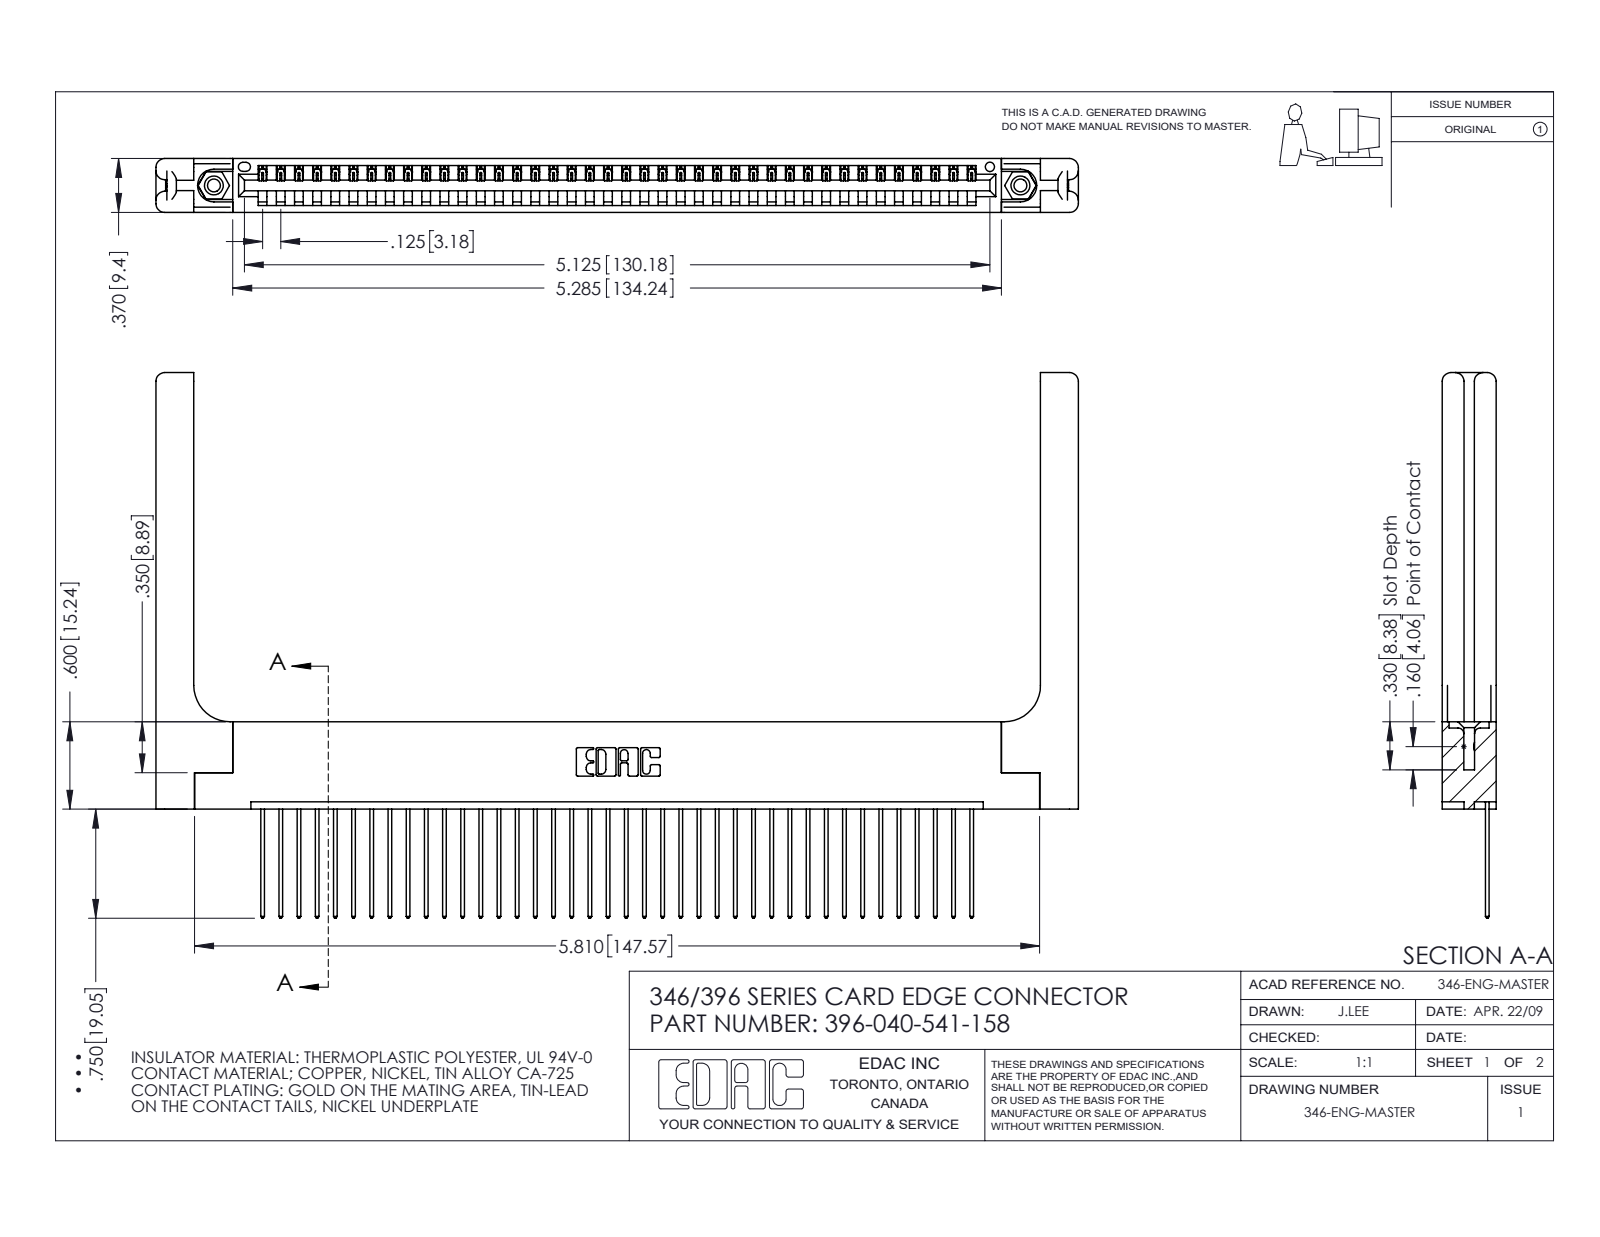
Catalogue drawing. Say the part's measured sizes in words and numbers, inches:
The part is named "345-250-001_345-250-001-102; 346-220-058_345-220-058; 346 Part_Flush Mounting Lugs - 0.156 Dia-TH; 345-292-001_345-293-141 (+1 more)". Its 3-D file was written by "SolidWorks 2016 (CONFIG_CONTROL_DESIGN)". It is 45 solids with 2698 faces: 1824 planar, 814 cylindrical and 60 other. Overall it measures 6.341 by 3.75 by 0.37 inches. Its volume is 1.407 cubic inches and its surface area 39.3 square inches. Round holes: 2 of diameter 0.089, 2 of diameter 0.125, 2 of diameter 0.156, 1 of diameter 0.064. Round bosses or shafts: 2 of diameter 0.155. Partial cylindrical surfaces (rounded edges, fillets, slot ends): 80 of radius 0.006, 80 of radius 0.01, 22 of radius 0.01, 16 of radius 0.06, 6 of radius 0.007, 6 of radius 0.031, 3 of radius 0.026, 2 of radius 0.03. The main face-to-face distances are 0.37, 0.048, 0.322, 0.072, 0.148, 0.15, 0.25, 0.298, 0.025, 0.222. The hole center spacings are 0.246, 5.336, 5.545.
